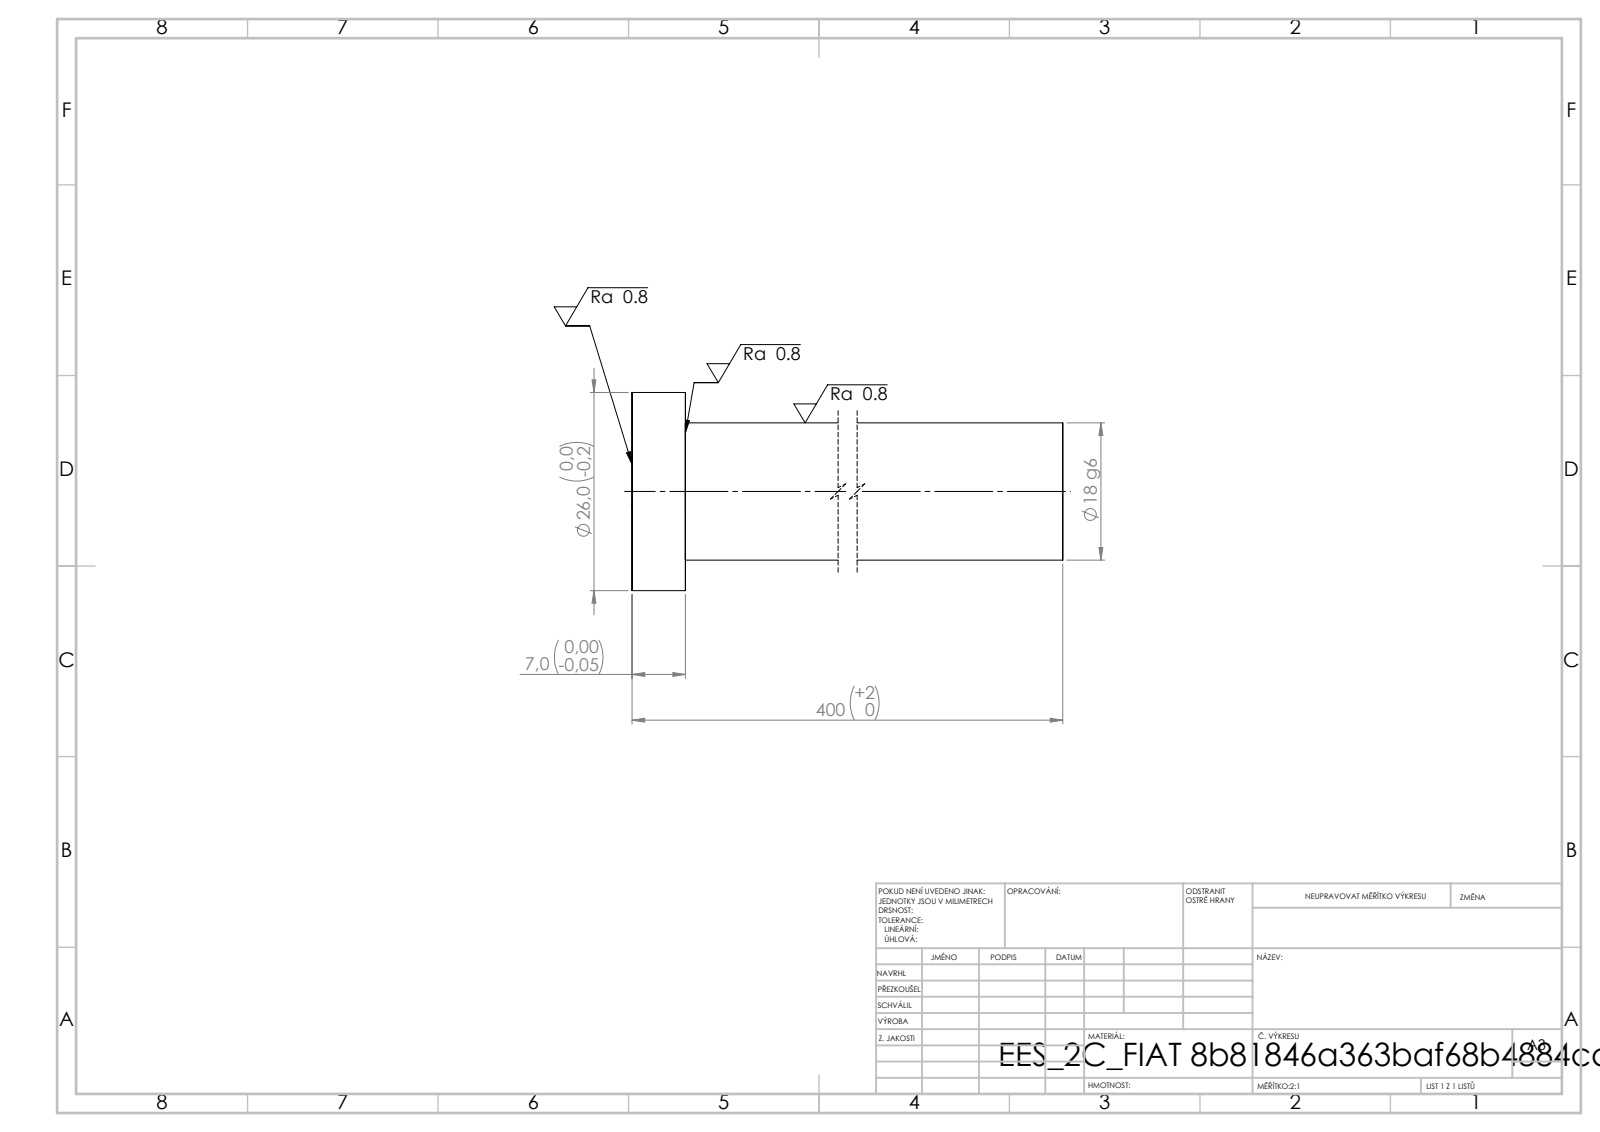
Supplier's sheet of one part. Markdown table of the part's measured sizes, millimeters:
| quantity | value |
| --- | --- |
| STEP written by | SolidWorks 2019 (CONFIG_CONTROL_DESIGN) |
| units | millimeters |
| bodies | 1 solid, 7 faces (3 planar, 4 cylindrical, 0 other) |
| overall size | 400 × 26 × 26 |
| volume | 103 723 mm³ |
| surface area | 23 857 mm² |
| round bosses / shafts (diameter × count) | 26 × 1, 18 × 1 |
| main face-to-face distances | 7, 400, 393 |
